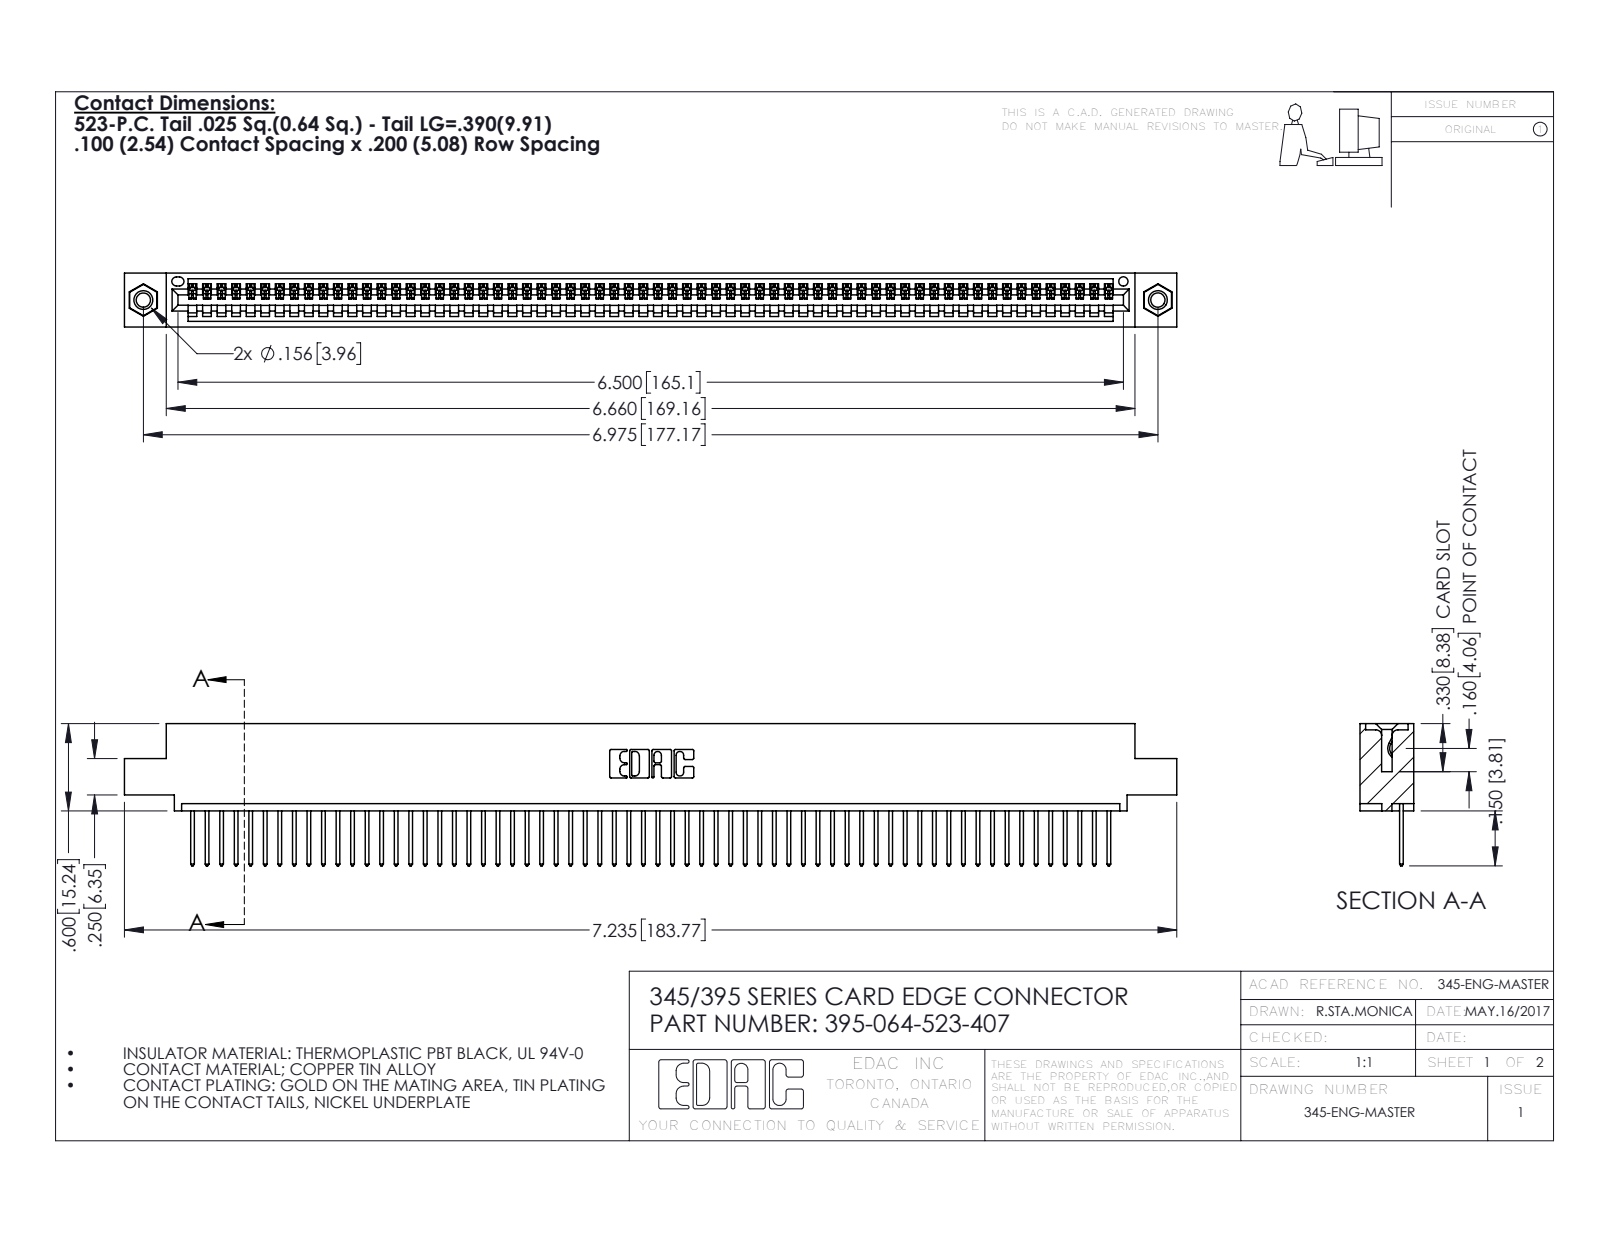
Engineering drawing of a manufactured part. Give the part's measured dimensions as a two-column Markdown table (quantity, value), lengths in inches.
| quantity | value |
| --- | --- |
| part name | 345-292-001_345-293-123; 345 Part_0.110 Offset - 0.156 Dia-TI; 345-250-001_345-250-005-103; 395-064-523-407 |
| STEP written by | SolidWorks 2016 (CONFIG_CONTROL_DESIGN) |
| units | inches |
| bodies | 67 solids, 3902 faces (2676 planar, 1210 cylindrical, 16 other) |
| overall size | 7.235 × 0.977 × 0.37 |
| volume | 1.069 in³ |
| surface area | 36.84 in² |
| round holes (diameter × count) | 0.098 × 2, 0.125 × 2, 0.156 × 2, 0.064 × 1 |
| round bosses / shafts (diameter × count) | 0.155 × 2 |
| partial cylindrical surfaces (radius × count) | 0.006 × 128, 0.01 × 128, 0.01 × 22, 0.007 × 6, 0.031 × 6, 0.026 × 3, 0.031 × 2, 0.04 × 2 |
| main face-to-face distances | 0.072, 0.298, 0.37, 0.098, 0.272, 0.025, 0.2, 0.225, 0.149, 0.072 |
| hole center spacings | 0.27, 6.739, 6.975 |
